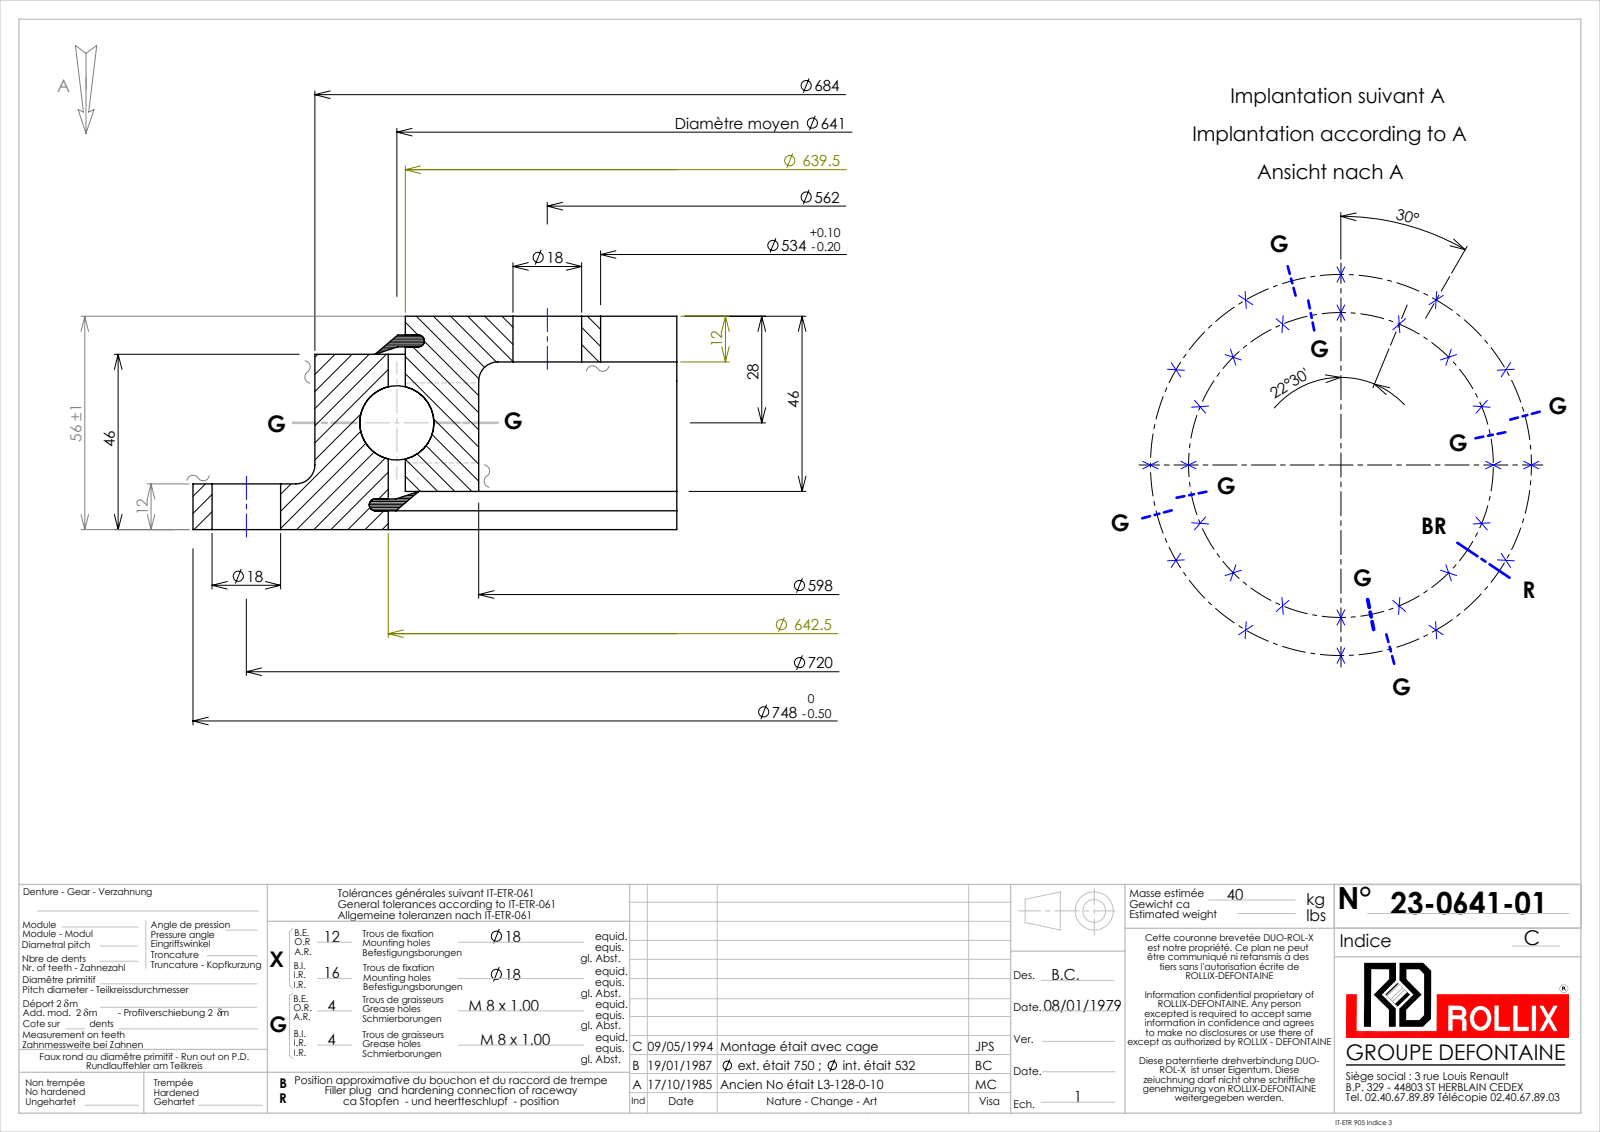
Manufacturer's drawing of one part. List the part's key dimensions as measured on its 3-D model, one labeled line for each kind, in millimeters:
Part name (STEP PRODUCT): 23-0641-01
STEP written by: SolidWorks 2016 (CONFIG_CONTROL_DESIGN)
Units: millimetres
Bodies: 13 solids, 314 faces (94 planar, 108 cylindrical, 112 other)
Overall size (bounding box): 748 × 748 × 56
Volume: 4 691 000 mm³ · Surface area: 969 957 mm²
Round holes (diameter × count): ⌀18 ×28, ⌀7 ×8, ⌀534 ×1, ⌀598 ×1, ⌀645.5 ×1
Round bosses / shafts (diameter × count): ⌀8 ×8, ⌀748 ×1, ⌀684 ×1, ⌀636.5 ×1
Main face-to-face distances: 12, 44, 56, 10, 46, 2, 34, 32, 36, 4.95
Hole centre spacings: 360, 109.64, 281, 312.23, 551.2, 186.35, 215.07, 397.39
